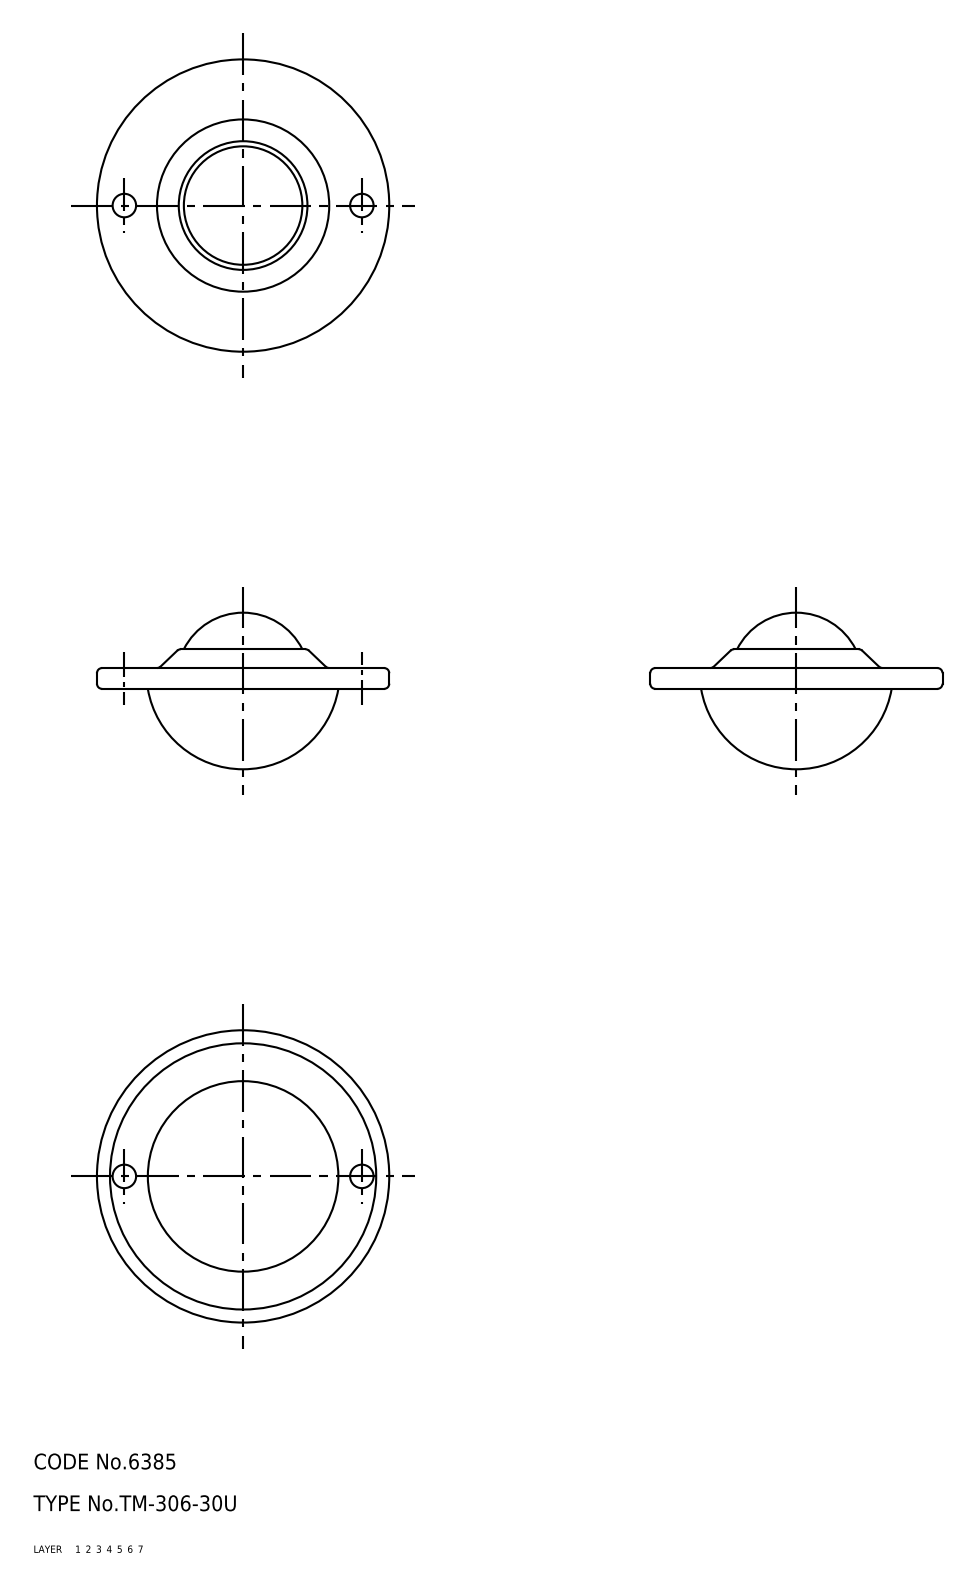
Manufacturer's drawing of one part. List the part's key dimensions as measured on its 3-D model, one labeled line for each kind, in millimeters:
Part name (STEP PRODUCT): 67112942; 67112955; 67112968
STEP written by: CADfix (AUTOMOTIVE_DESIGN)
Units: millimetres
Bodies: 3 solids, 44 faces (0 planar, 0 cylindrical, 44 other)
Overall size (bounding box): 56 × 56 × 30
Volume: 16 876 mm³ · Surface area: 14 435 mm²
